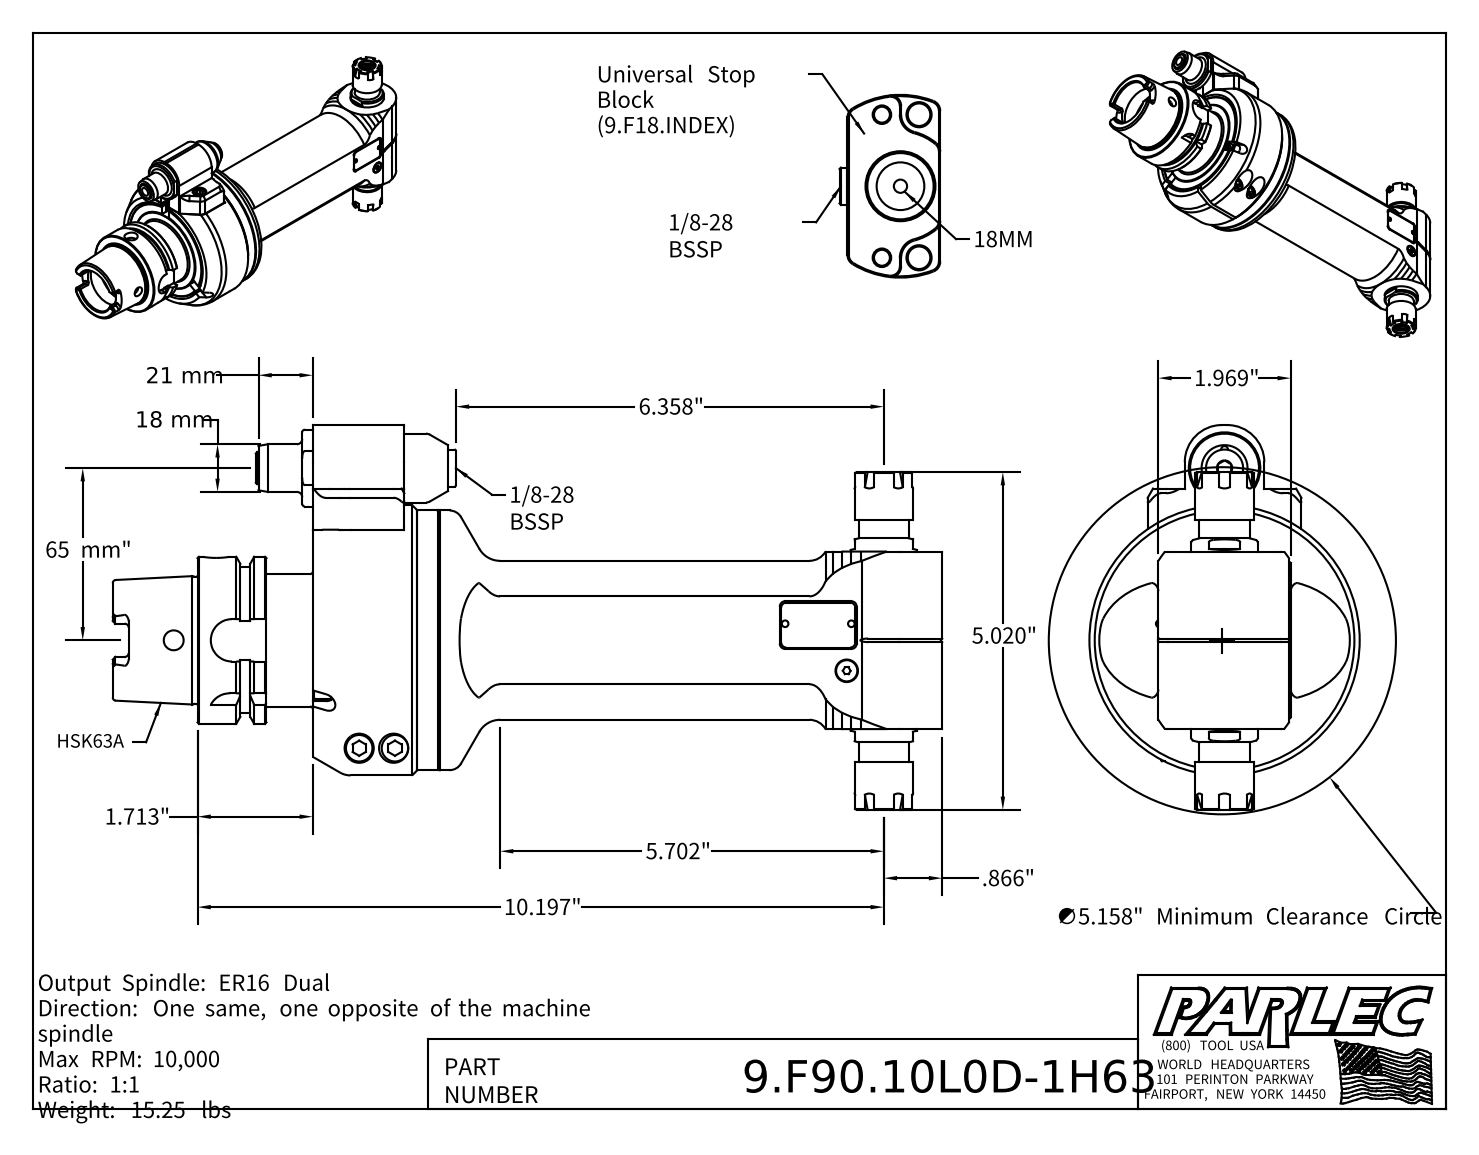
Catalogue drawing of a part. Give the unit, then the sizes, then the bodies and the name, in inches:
Units: inches
Overall size (bounding box): 12.323 × 5.719 × 4.016
Round holes (diameter × count): ⌀0.433 ×3, ⌀0.102 ×2, ⌀0.165 ×2, ⌀0.197 ×2, ⌀0.409 ×2, ⌀0.492 ×2, ⌀0.098 ×1, ⌀0.118 ×1, ⌀0.256 ×1, ⌀0.276 ×1, ⌀0.295 ×1, ⌀0.335 ×1
Round bosses / shafts (diameter × count): ⌀0.394 ×4, ⌀0.236 ×4, ⌀0.709 ×2, ⌀0.315 ×2, ⌀0.098 ×2, ⌀4.016 ×1, ⌀3.858 ×1, ⌀3.031 ×1
Partial cylindrical surfaces — rounded edges, fillets, slot ends (radius × count): R0.079 ×12, R0.059 ×6, R0.113 ×4, R0.157 ×4, R0.315 ×4, R0.016 ×2, R0.02 ×2, R0.039 ×2
Main face-to-face distances: 1.26, 1.969, 1.024, 0.02, 1.555, 0.276, 0.295, 0.984, 0.335, 0.059
Hole centre spacings: 0.276, 0.051, 0.512, 0.551, 1.72, 2.208, 2.283, 2.559
Volume: 66.98 in³ · Surface area: 241.7 in²
Bodies: 5 solids, 598 faces (296 planar, 136 cylindrical, 166 other)
Part name (STEP PRODUCT): 9.F90.10L0D-1H63; 9_F90_10L00_2U; 9_GA1_566_2 (Type 1, H63A, 65mm)
STEP written by: Autodesk Inventor 2022 (AUTOMOTIVE_DESIGN)
